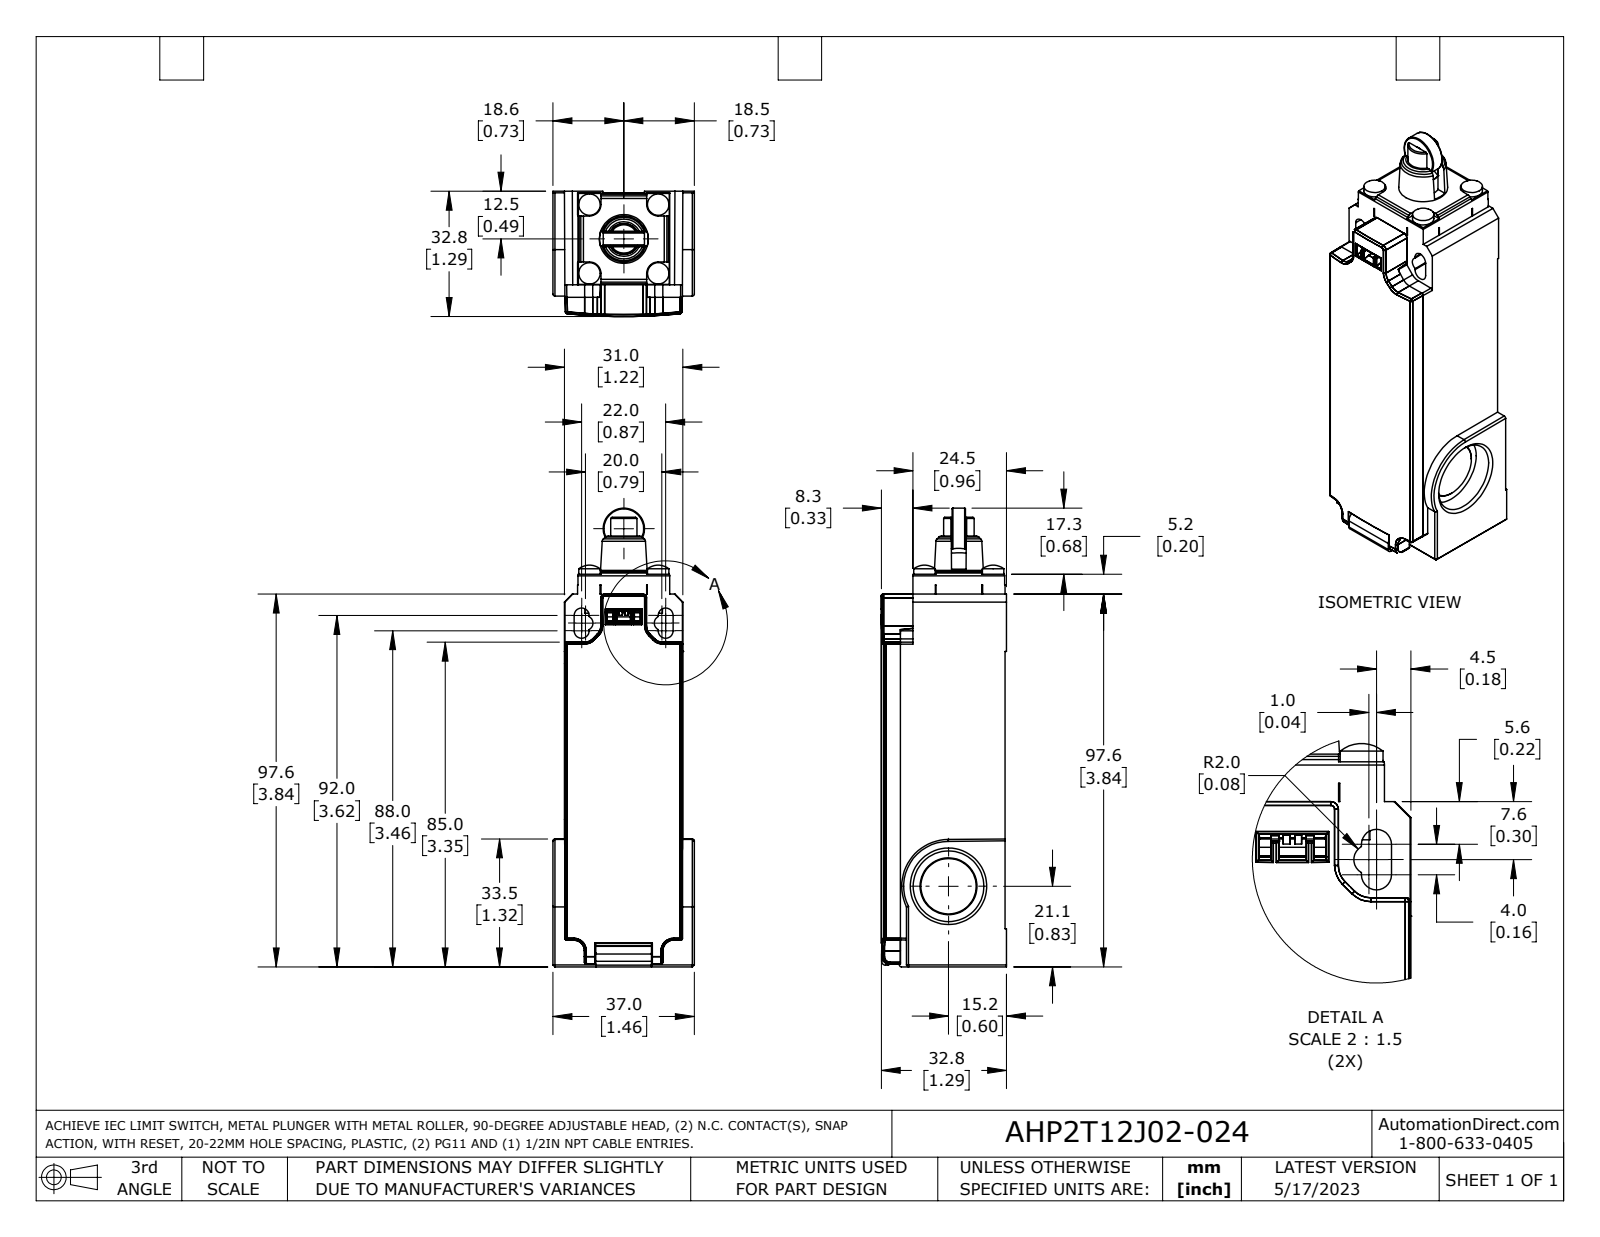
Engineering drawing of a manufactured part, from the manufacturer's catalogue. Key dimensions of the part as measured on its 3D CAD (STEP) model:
Part name (STEP PRODUCT): AHP2T12J02-024
STEP written by: SolidWorks 2021 (AUTOMOTIVE_DESIGN)
Units: inches
Bodies: 1 solid, 577 faces (332 planar, 160 cylindrical, 85 other)
Overall size (bounding box): 4.728 × 1.457 × 1.291
Volume: 5.795 in³ · Surface area: 37.12 in²
Round holes (diameter × count): ⌀0.091 ×4, ⌀0.118 ×4, ⌀0.728 ×2, ⌀0.319 ×1, ⌀0.86 ×1
Round bosses / shafts (diameter × count): ⌀0.22 ×5, ⌀0.425 ×1, ⌀0.315 ×1, ⌀0.118 ×1
Partial cylindrical surfaces — rounded edges, fillets, slot ends (radius × count): R0.012 ×41, R0.02 ×34, R0.039 ×12, R0.118 ×8, R0.031 ×3, R0.008 ×2, R0.079 ×2, R0.11 ×2
Main face-to-face distances: 0.047, 1.138, 1.185, 1.457, 0.965, 0.236, 0.949, 0.016, 1.154, 1.201
Hole centre spacings: 0.709, 0.431, 0.501, 0.583, 1.002, 0.106, 0.498, 0.504
